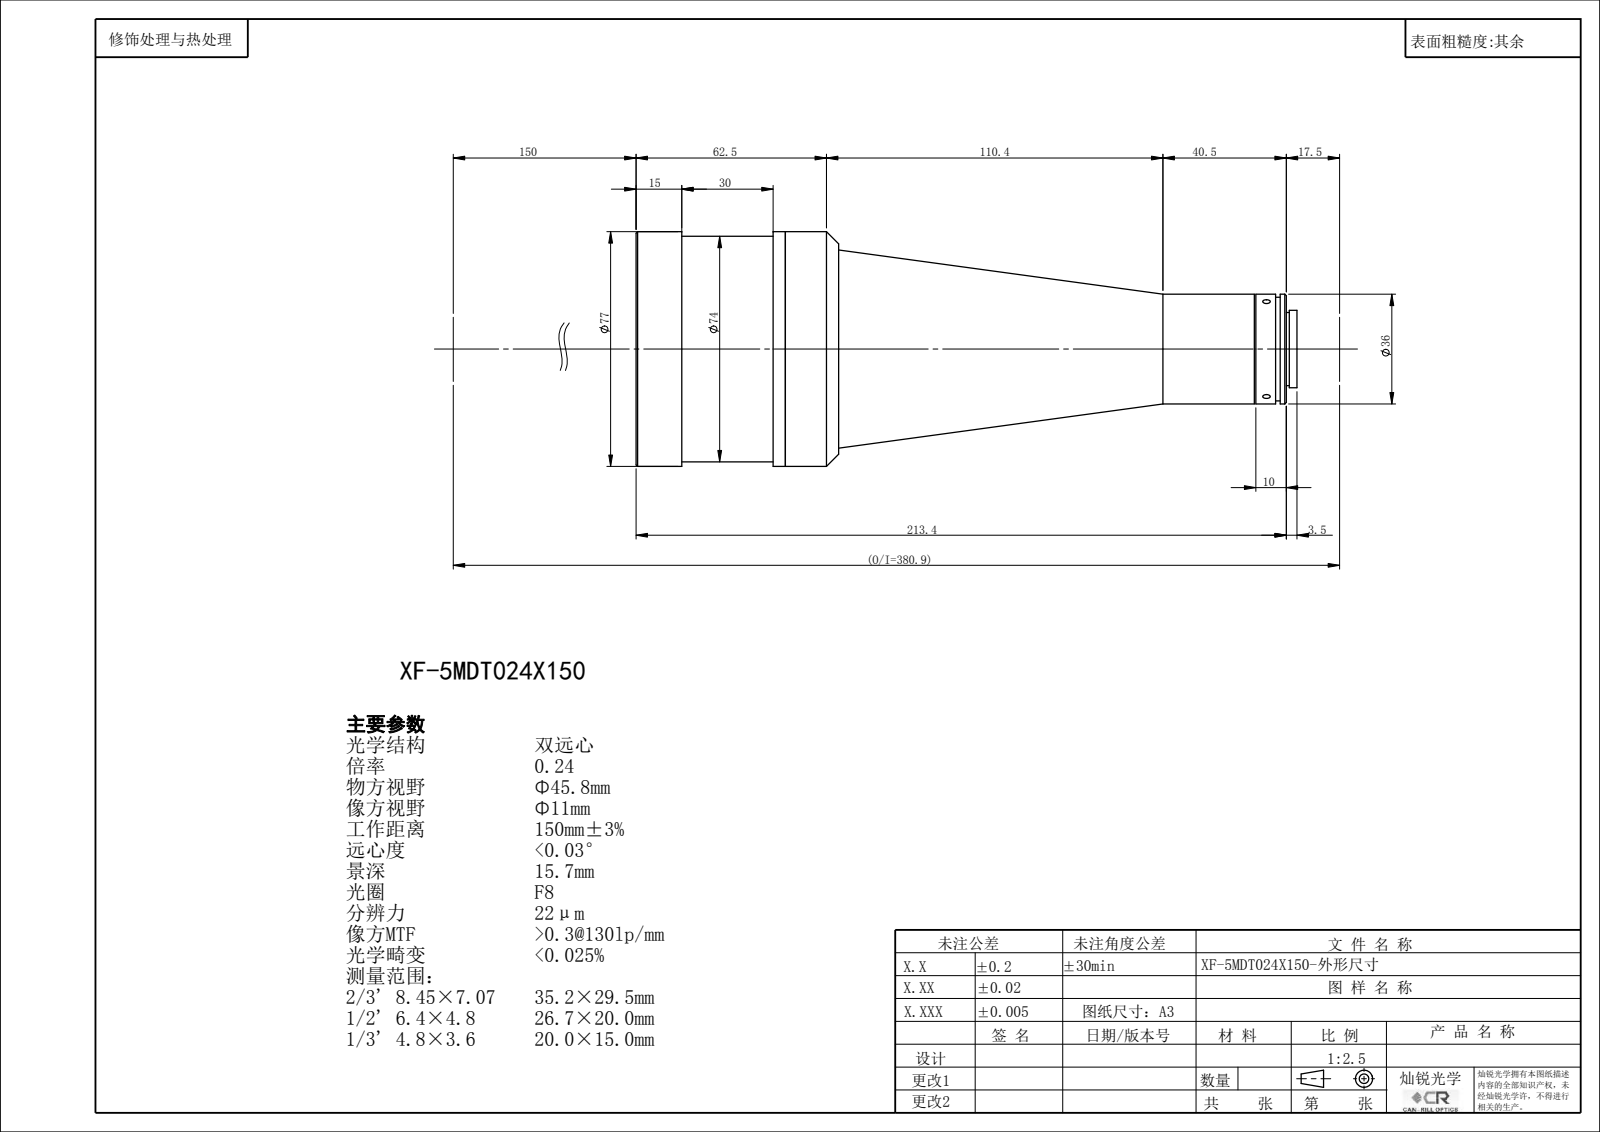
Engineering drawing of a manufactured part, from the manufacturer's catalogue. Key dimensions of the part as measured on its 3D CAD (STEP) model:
Part name (STEP PRODUCT): XF-5MDT024X150
STEP written by: SolidWorks 2014 (CONFIG_CONTROL_DESIGN)
Units: millimetres
Bodies: 0 solids, 91 faces (37 planar, 40 cylindrical, 14 other)
Overall size (bounding box): 216.94 × 77 × 77
Round holes (diameter × count): ⌀2.5 ×3, ⌀16 ×1, ⌀19.4 ×1, ⌀21 ×1, ⌀21.4 ×1, ⌀63 ×1, ⌀70 ×1
Round bosses / shafts (diameter × count): ⌀77 ×1, ⌀74 ×1, ⌀65 ×1, ⌀36 ×1, ⌀34 ×1, ⌀25.4 ×1, ⌀24 ×1
Main face-to-face distances: 49, 2, 211.44, 162.44, 213.44, 164.44, 3.33, 45.67, 208.11, 210.11
